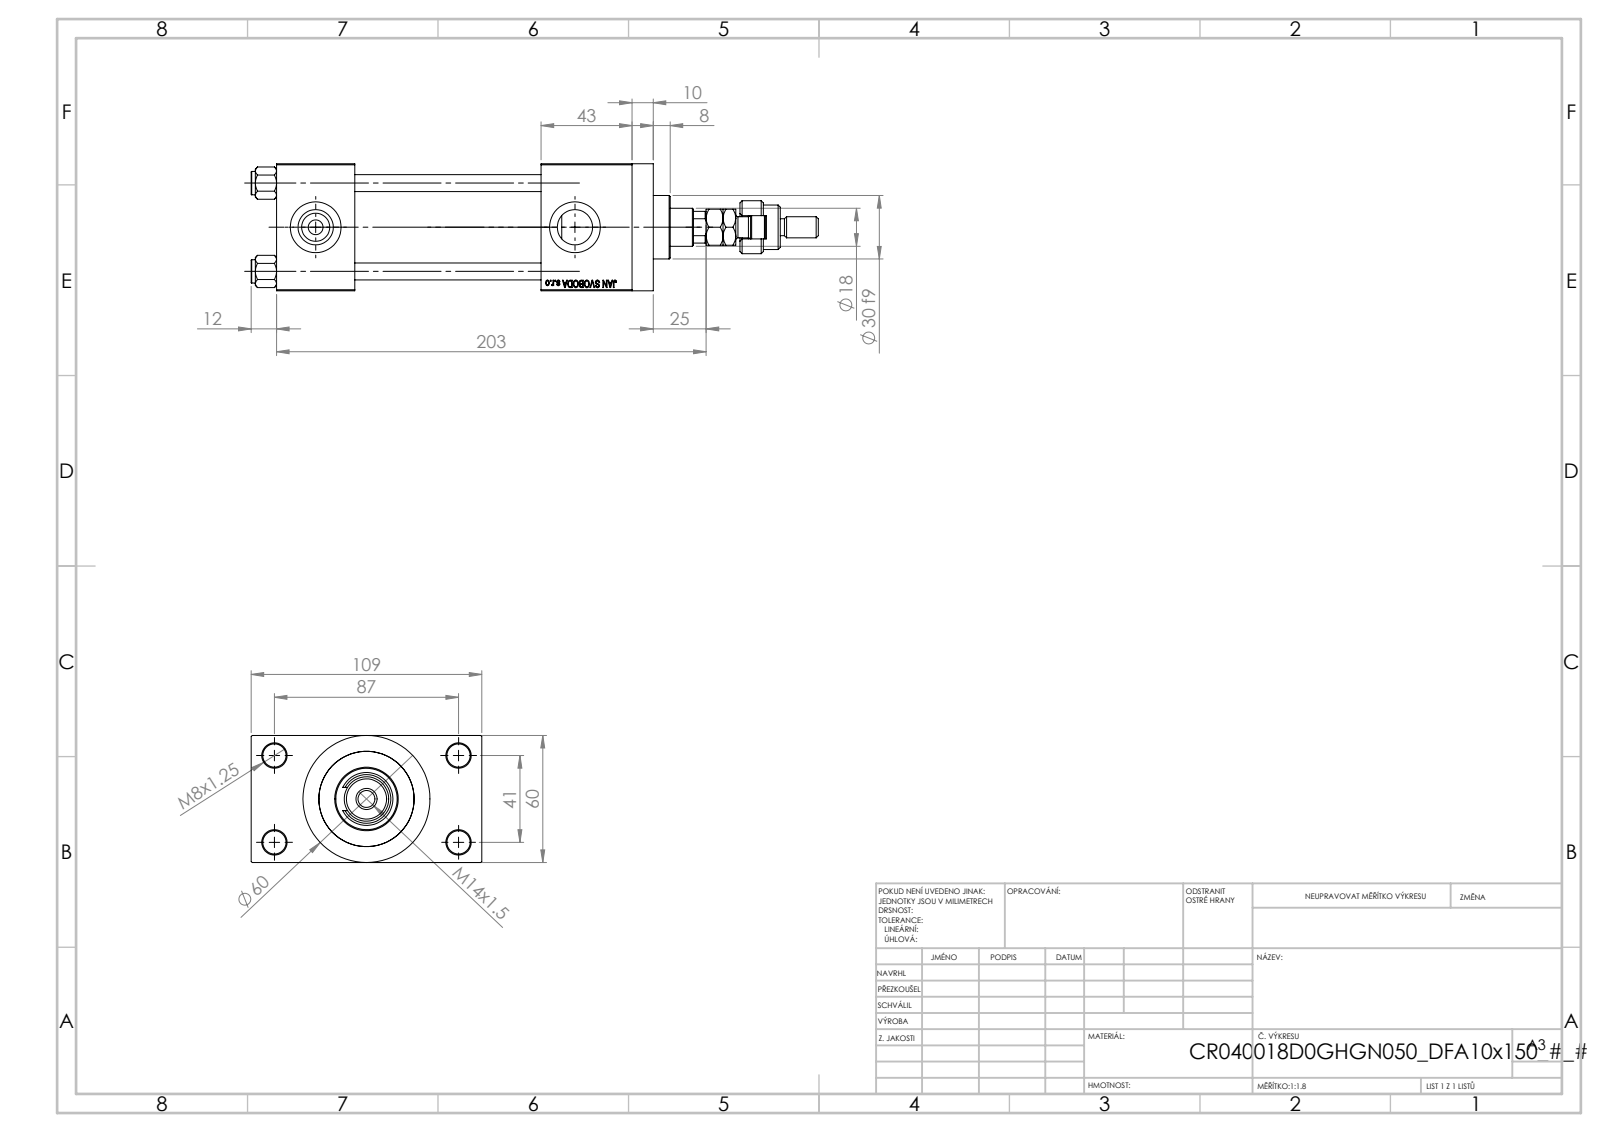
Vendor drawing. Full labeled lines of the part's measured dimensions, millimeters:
Part name (STEP PRODUCT): FEMALE_PART_FOR_DFA; V215CR_D_Body; NUT_M5_D; MFA (+3 more)
STEP written by: SolidWorks 2019 (CONFIG_CONTROL_DESIGN)
Units: millimetres
Bodies: 13 solids, 1189 faces (526 planar, 101 cylindrical, 562 other)
Overall size (bounding box): 268 × 109 × 60
Volume: 550 141 mm³ · Surface area: 140 809 mm²
Round holes (diameter × count): ⌀8 ×4, ⌀11 ×4, ⌀7 ×2, ⌀16.66 ×2, ⌀24 ×2, ⌀8.5 ×1, ⌀18 ×1, ⌀21 ×1, ⌀31 ×1, ⌀40 ×1, ⌀45 ×1
Round bosses / shafts (diameter × count): ⌀11 ×4, ⌀60 ×1, ⌀46 ×1, ⌀30 ×1, ⌀25 ×1, ⌀16 ×1, ⌀10 ×1, ⌀8 ×1
Partial cylindrical surfaces — rounded edges, fillets, slot ends (radius × count): R5.5 ×1, R8.5 ×1, R8.75 ×1
Main face-to-face distances: 60, 24.5, 88, 84.5, 37, 125, 168, 131, 43, 53
Hole centre spacings: 22.65, 29.49, 41.7, 47.15, 48.09, 64.35, 76.49, 41
